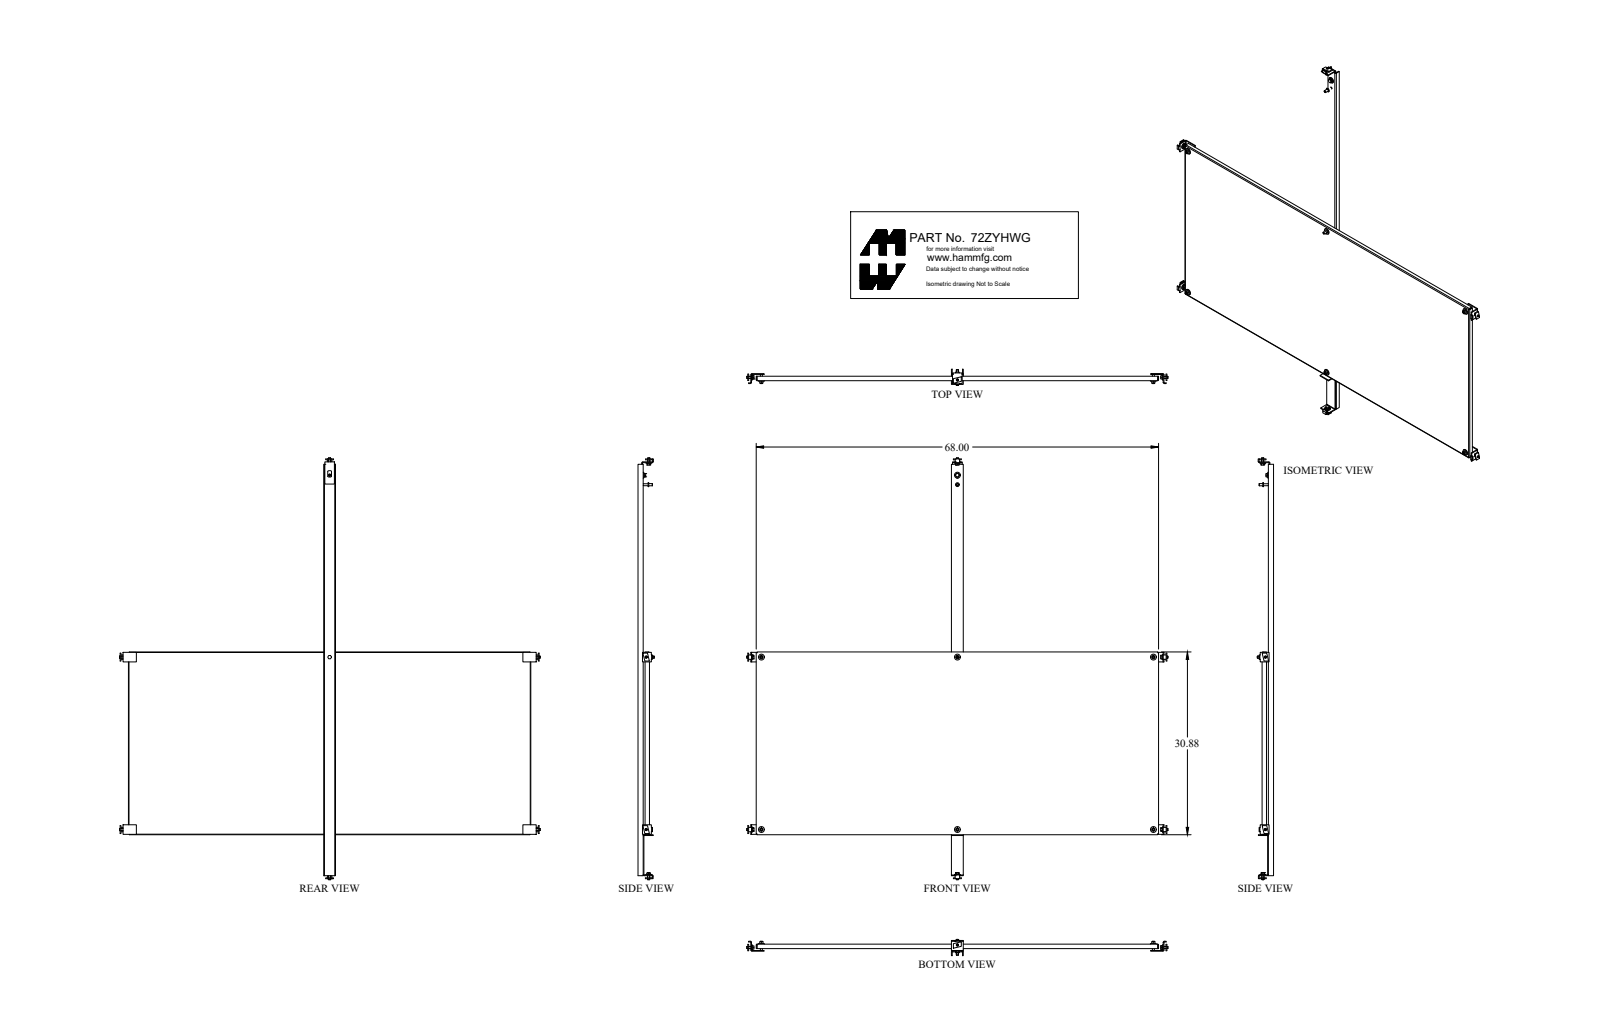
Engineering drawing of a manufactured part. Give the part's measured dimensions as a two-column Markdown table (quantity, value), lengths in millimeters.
| quantity | value |
| --- | --- |
| part name | 72ZYHWG_Default |
| STEP written by | SolidWorks 2018 (CONFIG_CONTROL_DESIGN) |
| units | millimeters |
| bodies | 14 solids, 305 faces (152 planar, 105 cylindrical, 48 other) |
| overall size | 1801 × 1792.8 × 65.9 |
| volume | 4 062 000 mm³ |
| surface area | 3 277 000 mm² |
| round holes (diameter × count) | 14.3 × 6, 11.1 × 5, 11.1 × 1, 11.5 × 1 |
| round bosses / shafts (diameter × count) | 16.5 × 6, 8.4 × 6, 9.5 × 4, 9.5 × 2 |
| partial cylindrical surfaces (radius × count) | 1.5 × 11, 4.7 × 11, 1.2 × 4, 3.6 × 4, 5.6 × 2 |
| main face-to-face distances | 2.4, 3.2, 30.1, 27, 24.6, 27.7, 781.8, 3.2, 50.8, 47.6 |
| hole center spacings | 1120.3, 739.8, 841.4, 841.4, 1682.8, 1838.2, 0.8, 739.9 |
